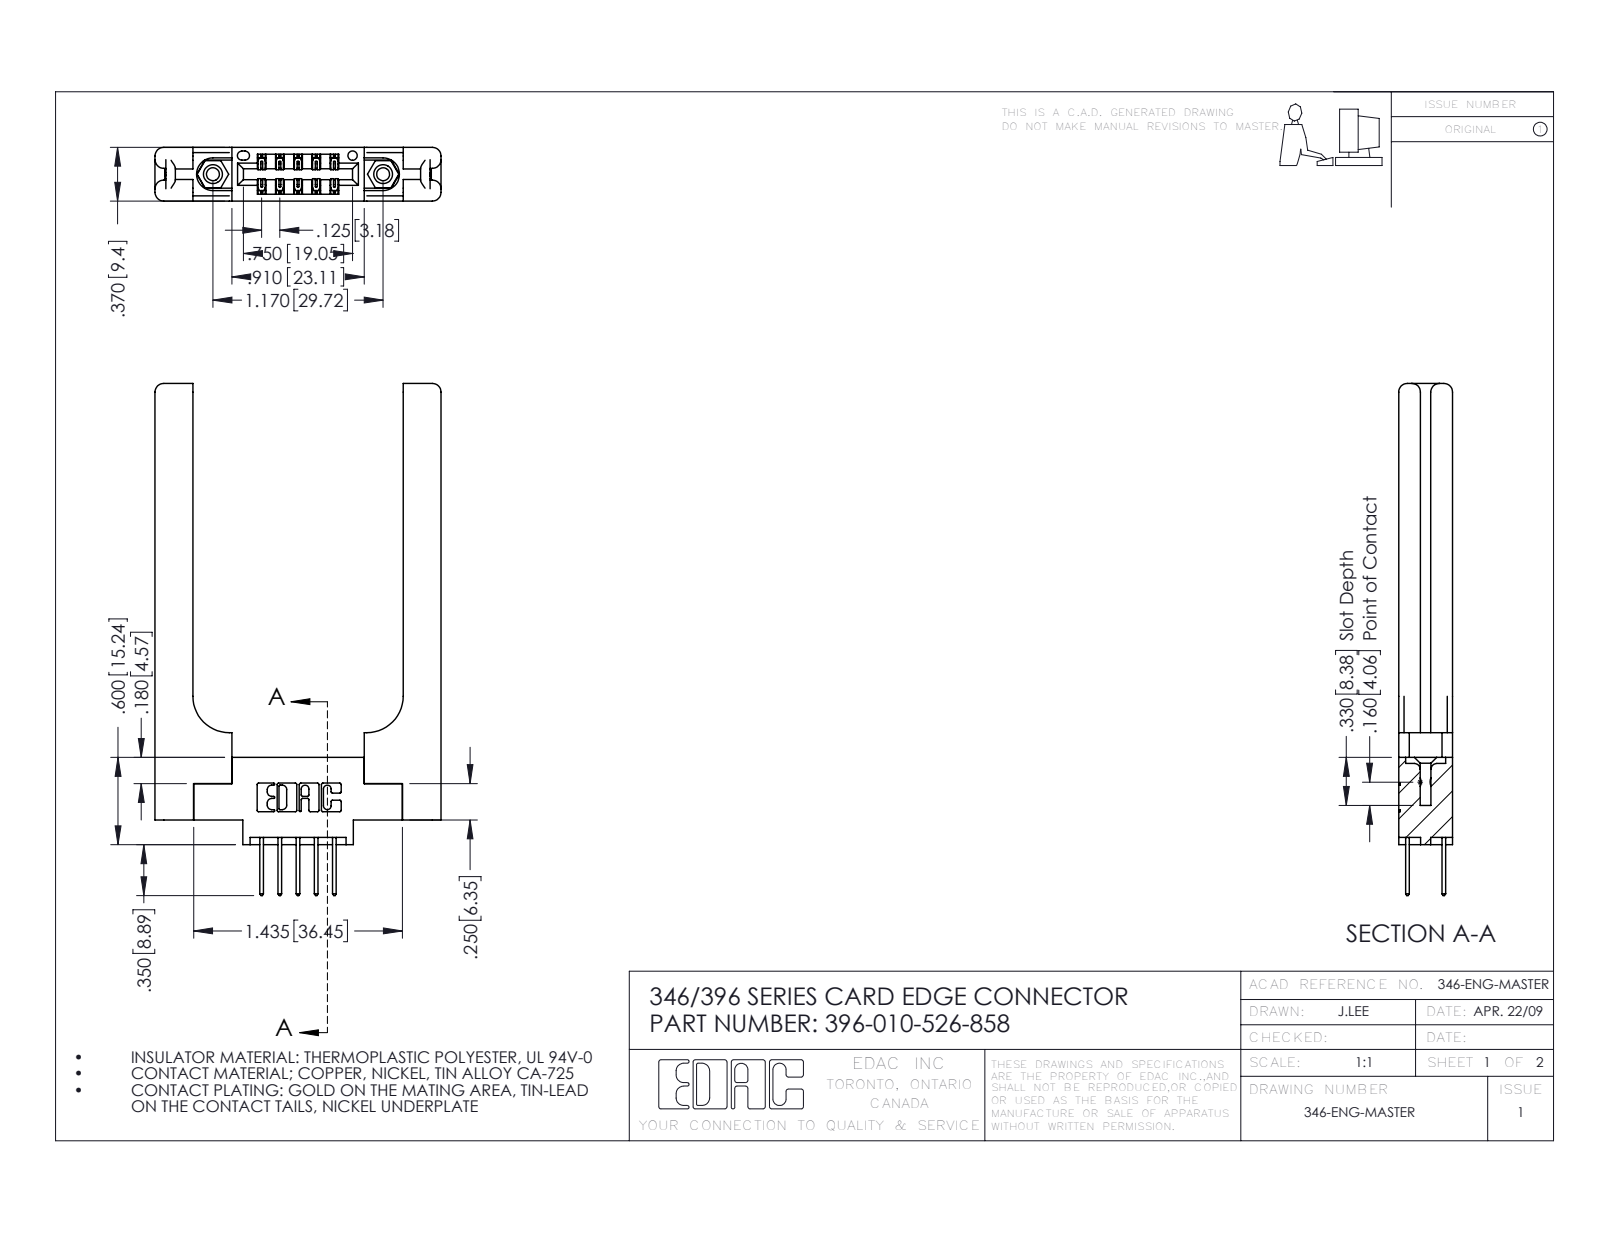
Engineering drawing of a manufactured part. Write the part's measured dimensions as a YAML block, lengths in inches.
part_name: "345-292-001_345-293-126; 346-220-058_345-220-058; 345-250-001_345-250-001-102; 346 Part_0.170 Offset - 0.156 Dia-TH (+1 more)"
step_written_by: "SolidWorks 2016 (CONFIG_CONTROL_DESIGN)"
units: inches
bodies: {solids: 15, faces: 902, planar: 578, cylindrical: 264, other: 60}
overall_size: [3.52, 1.966, 0.37]
volume: 0.729
surface_area: 16.67
round_holes:
  - {diameter: 0.089, count: 2}
  - {diameter: 0.125, count: 2}
  - {diameter: 0.156, count: 2}
  - {diameter: 0.064, count: 1}
round_bosses_or_shafts:
  - {diameter: 0.155, count: 2}
partial_cylinders:
  - {radius: 0.01, count: 22}
  - {radius: 0.06, count: 16}
  - {radius: 0.006, count: 15}
  - {radius: 0.01, count: 10}
  - {radius: 0.007, count: 6}
  - {radius: 0.031, count: 6}
  - {radius: 0.026, count: 3}
  - {radius: 0.014, count: 2}
face_to_face_distances: [0.37, 0.15, 0.22, 0.25, 0.072, 0.148, 1.446, 0.075, 0.102, 0.048]
hole_center_spacings: [0.246, 0.969, 1.17]
